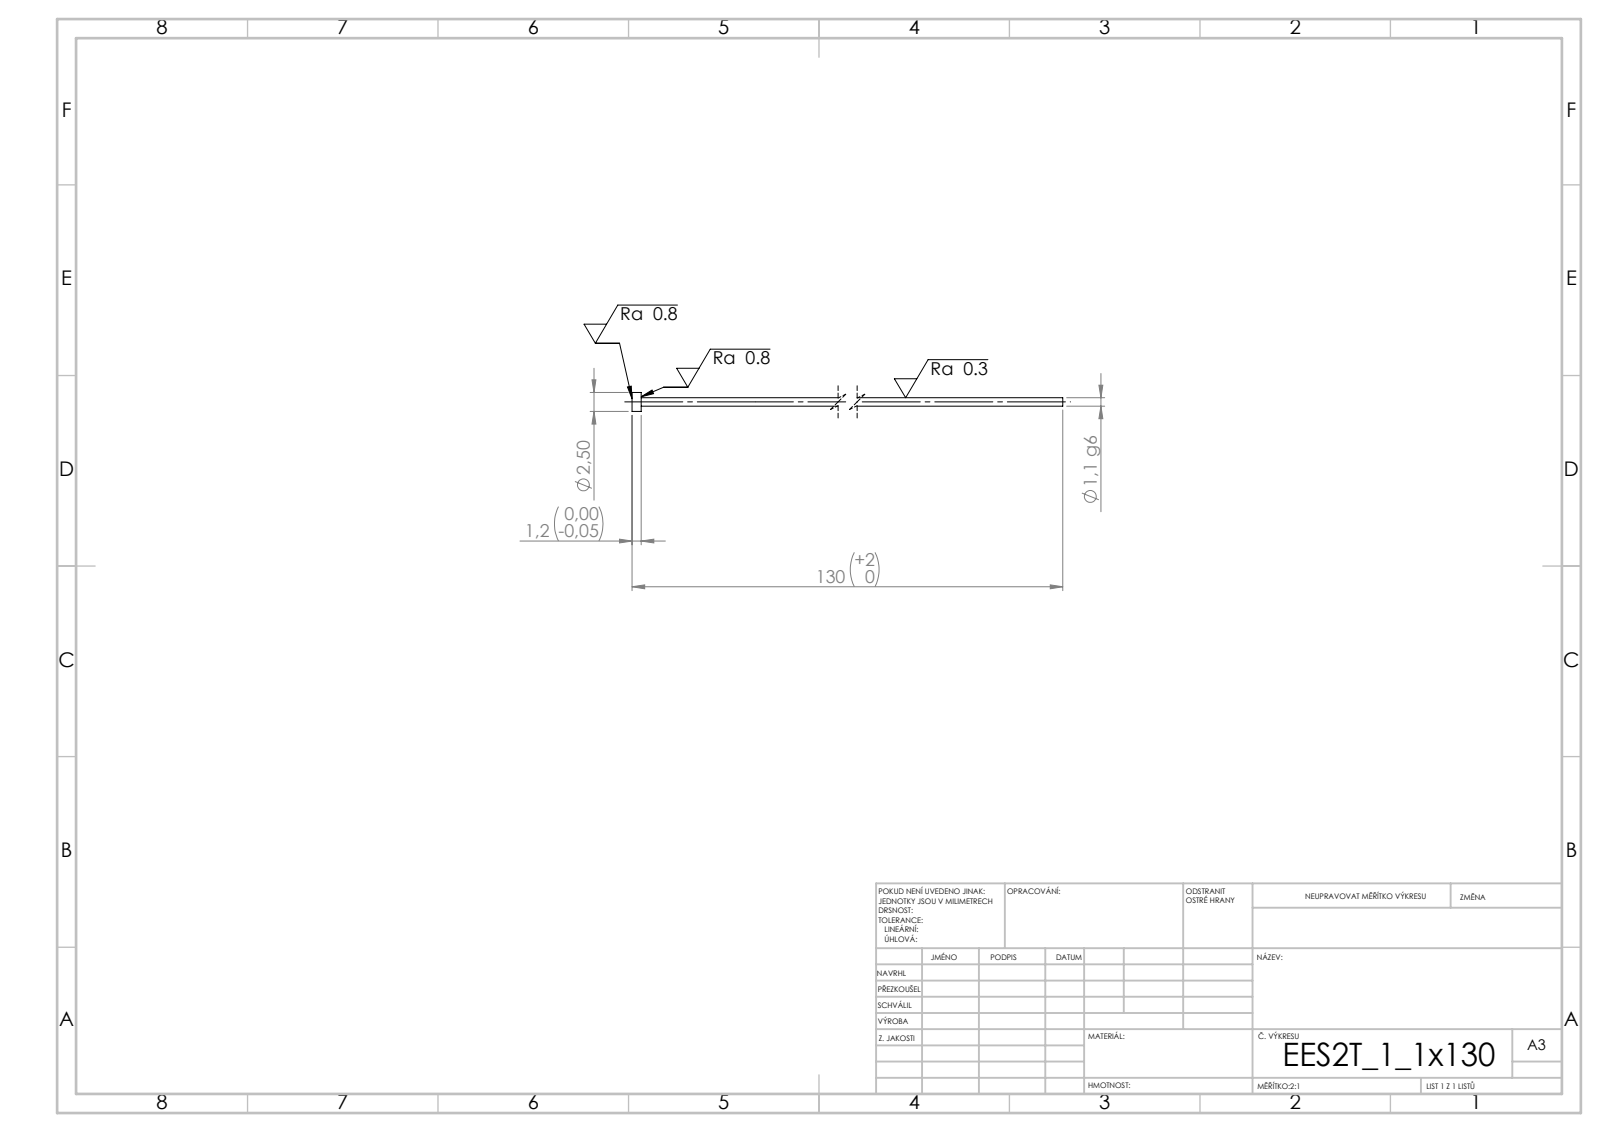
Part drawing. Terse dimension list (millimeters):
written by: SolidWorks 2019 (CONFIG_CONTROL_DESIGN)
unit: mm
bodies: 1 solid, 7 faces (3 planar, 4 cylindrical, 0 other)
size: 130 × 2.5 × 2.5
volume: 128 mm³; area: 464 mm²
bosses: 1× ⌀2.5, 1× ⌀1.1
face distances: 1.2, 130, 128.8
